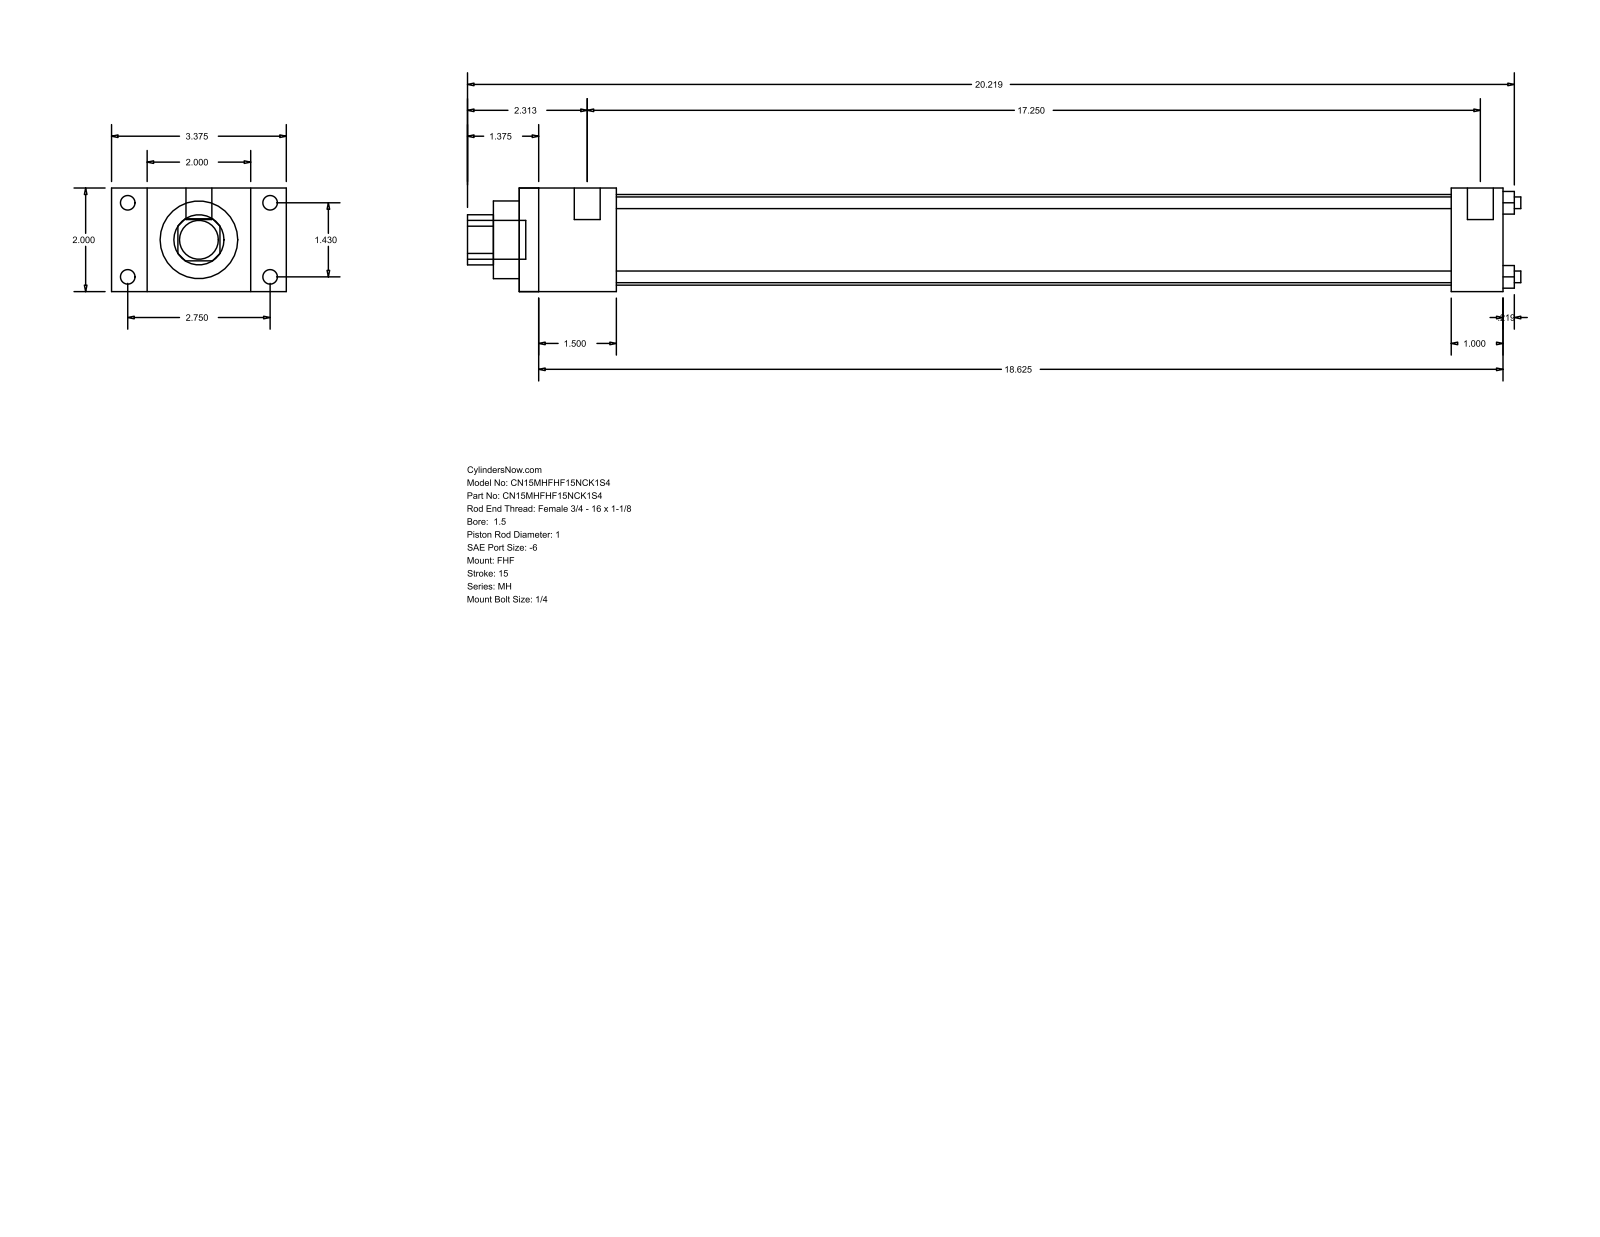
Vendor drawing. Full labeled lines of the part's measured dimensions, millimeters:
Part name (STEP PRODUCT): MH_FHF__0150_1
STEP written by: GSSL Pune (CONFIG_CONTROL_DESIGN)
Units: millimetres
Bodies: 0 solids, 88 faces (60 planar, 28 cylindrical, 0 other)
Overall size (bounding box): 516.73 × 85.72 × 50.8
Round holes (diameter × count): ⌀5.71 ×4, ⌀25.4 ×1, ⌀38.1 ×1, ⌀44.45 ×1
Round bosses / shafts (diameter × count): ⌀7.14 ×4, ⌀5.56 ×4, ⌀12.7 ×2, ⌀19.05 ×1
Partial cylindrical surfaces — rounded edges, fillets, slot ends (radius × count): R12.29 ×1
Main face-to-face distances: 50.8, 17.46, 68.26, 47.63, 85.72, 482.6, 434.97, 25.4, 457.2, 409.57
Hole centre spacings: 25.68, 36.32, 51.36
